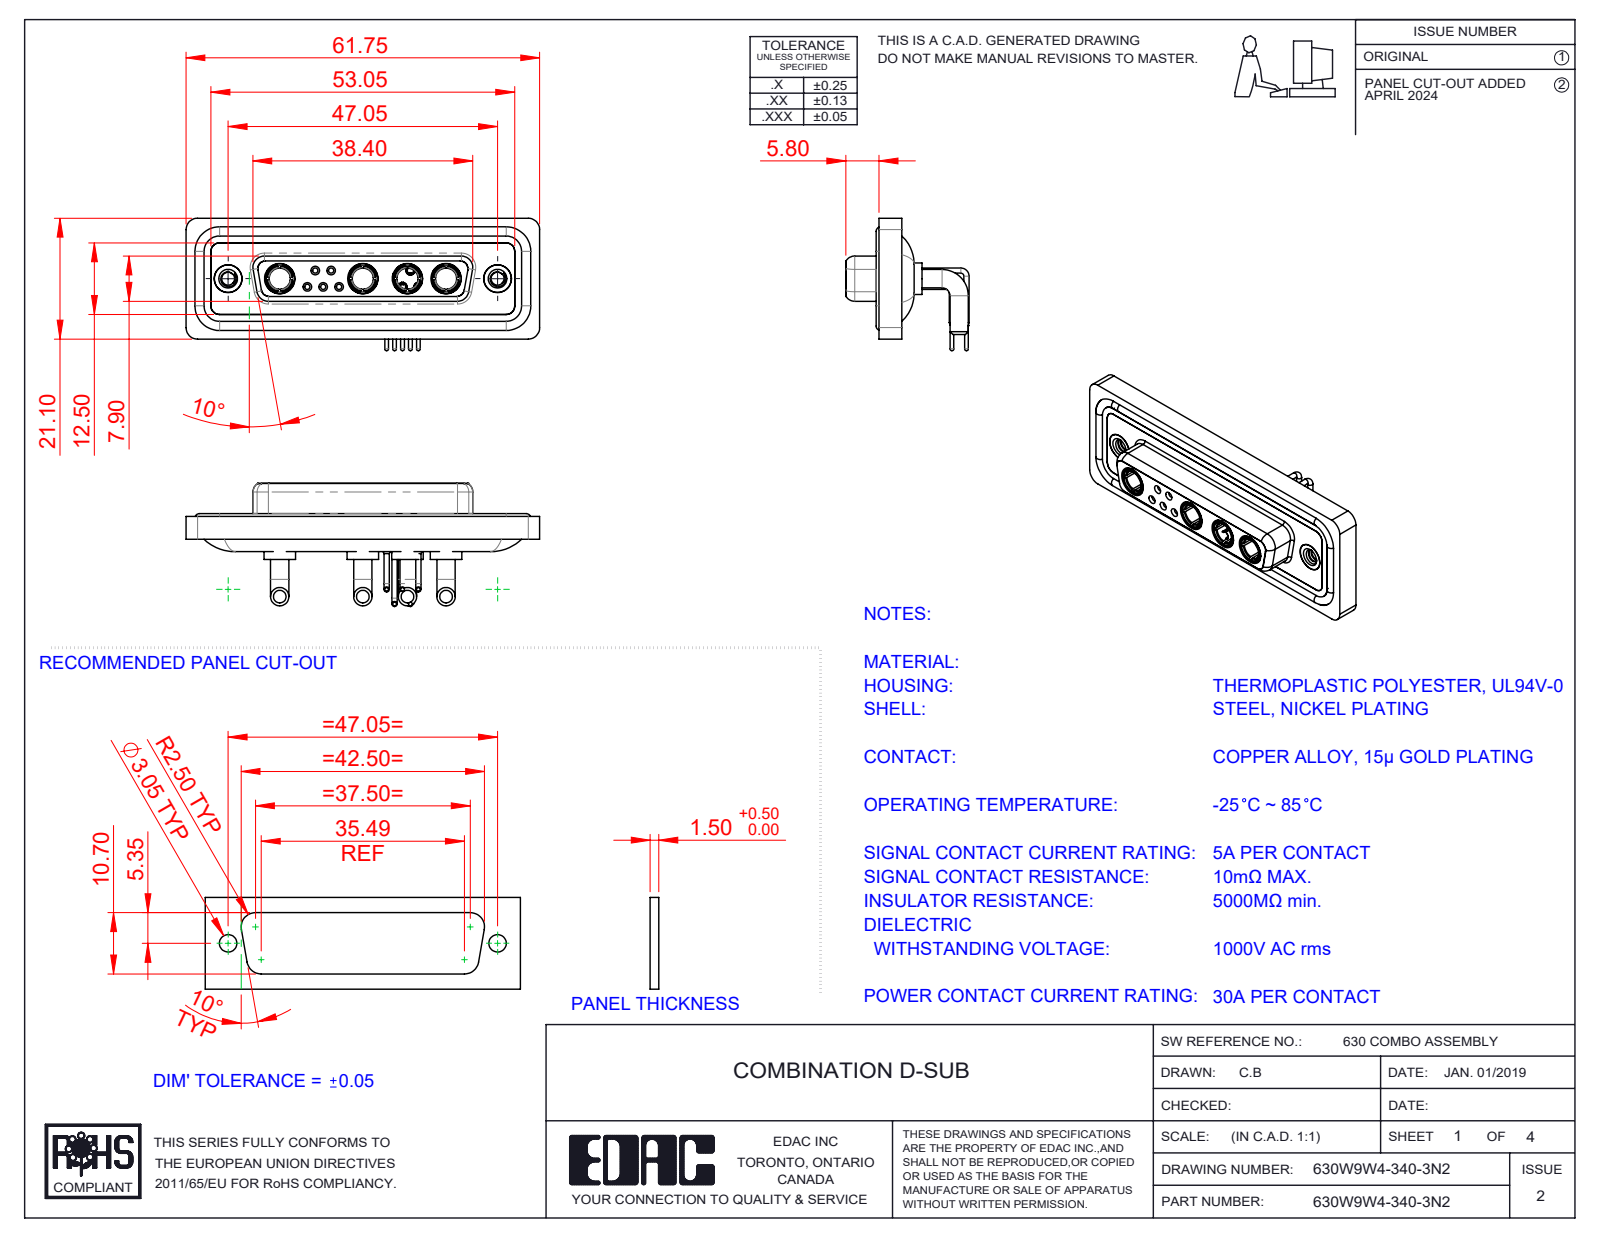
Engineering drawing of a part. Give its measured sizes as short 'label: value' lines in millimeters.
name: 630Combo Contact Row 2_50 Contacts; 630Combo Housing_9W4; 630W9W4-340-3N2; 630Combo Shell Front_25 Contacts (+5 more)
written by: SolidWorks 2023 (CONFIG_CONTROL_DESIGN)
unit: mm
bodies: 20 solids, 963 faces (296 planar, 403 cylindrical, 264 other)
size: 61.75 × 23.12 × 21.53
volume: 8 563 mm³; area: 14 120 mm²
holes: 6× ⌀4.85, 5× ⌀0.9, 5× ⌀1.1, 5× ⌀1.5, 5× ⌀2, 4× ⌀3.7, 4× ⌀5.3, 3× ⌀1.6, 2× ⌀1.7, 2× ⌀2.26, 2× ⌀4, 2× ⌀4.05
bosses: 10× ⌀0.9, 9× ⌀1.6, 8× ⌀3.2, 5× ⌀2, 5× ⌀1.5, 5× ⌀0.65, 4× ⌀5.5, 4× ⌀5.2
rounds: 18× R1.5, 18× R2, 8× R1.35, 8× R1.6, 4× R0.25, 4× R0.5, 4× R0.6, 4× R0.65
face distances: 0.4, 1.8, 4.1, 1.1, 1.6, 1.5, 2.5, 3.1, 3.7, 1.4
hole spacings: 3.16, 2.77, 5.04, 13.85, 11.08, 12.79, 15.5, 5.54
